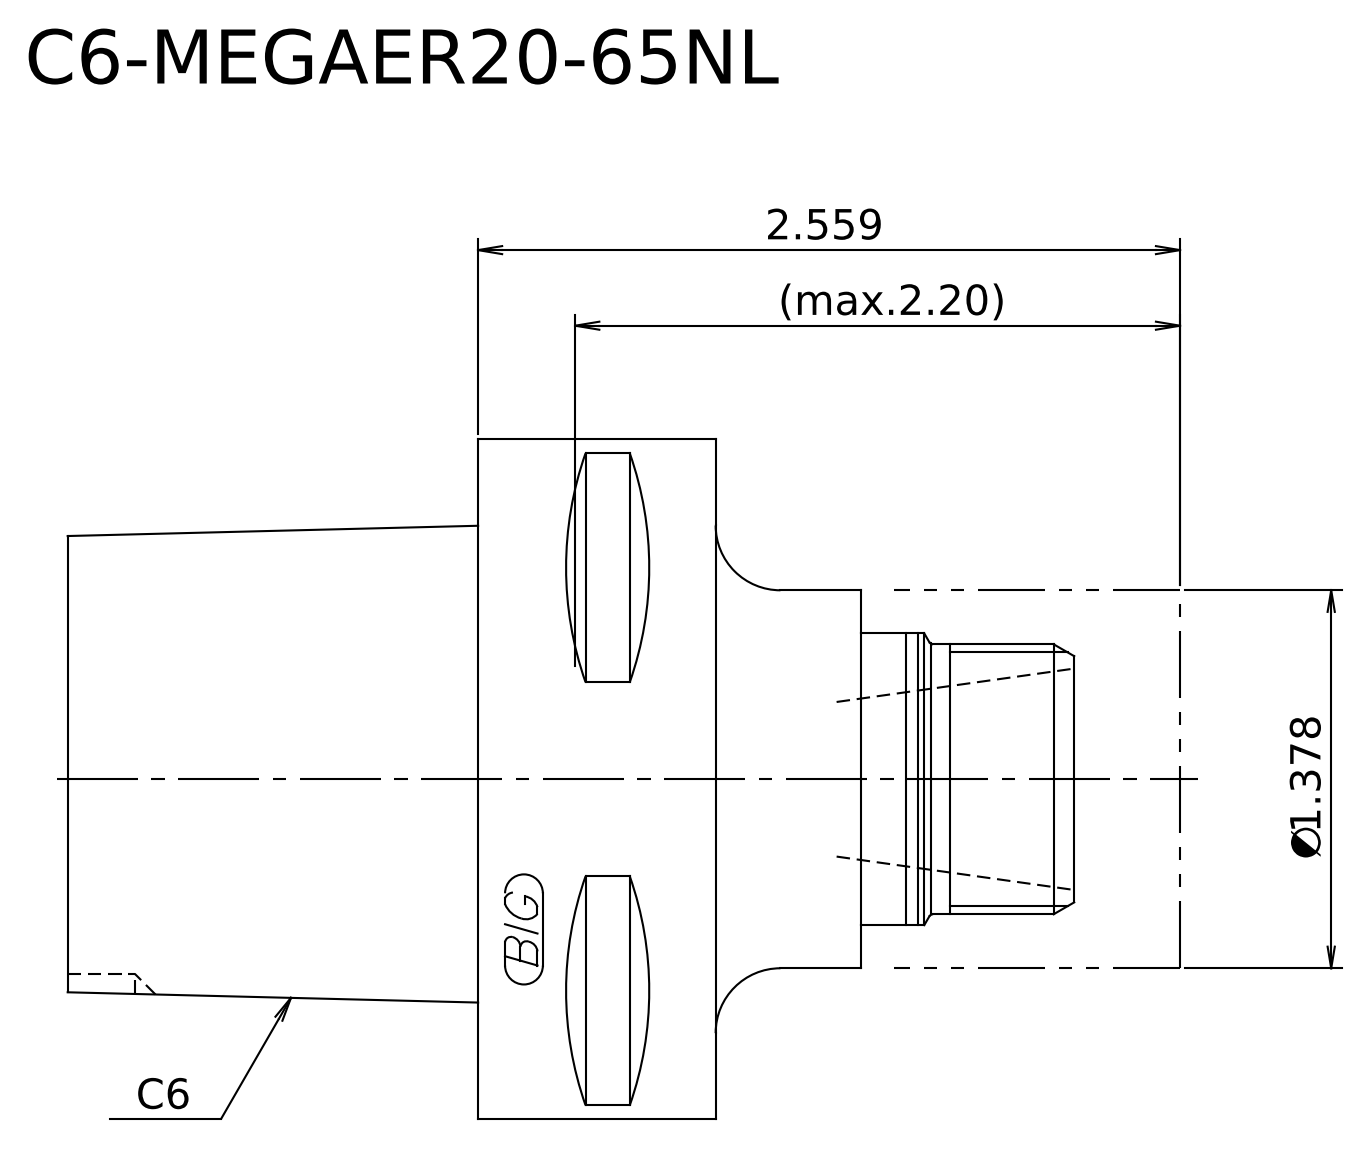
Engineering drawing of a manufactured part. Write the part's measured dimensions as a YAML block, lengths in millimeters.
step_written_by: "Kubotek KeyCreator 2011 V10.0.2 (22737) (automotive_design)"
units: millimeters
bodies: {solids: 2, faces: 18, planar: 7, cylindrical: 5, other: 6}
overall_size: [103, 63, 63]
volume: 174133
surface_area: 23085
round_bosses_or_shafts:
  - {diameter: 63, count: 1}
  - {diameter: 35, count: 1}
  - {diameter: 27, count: 1}
  - {diameter: 25, count: 1}
face_to_face_distances: [22, 60, 38, 16.5, 38.5, 76.5, 26.5, 43, 65, 103]
